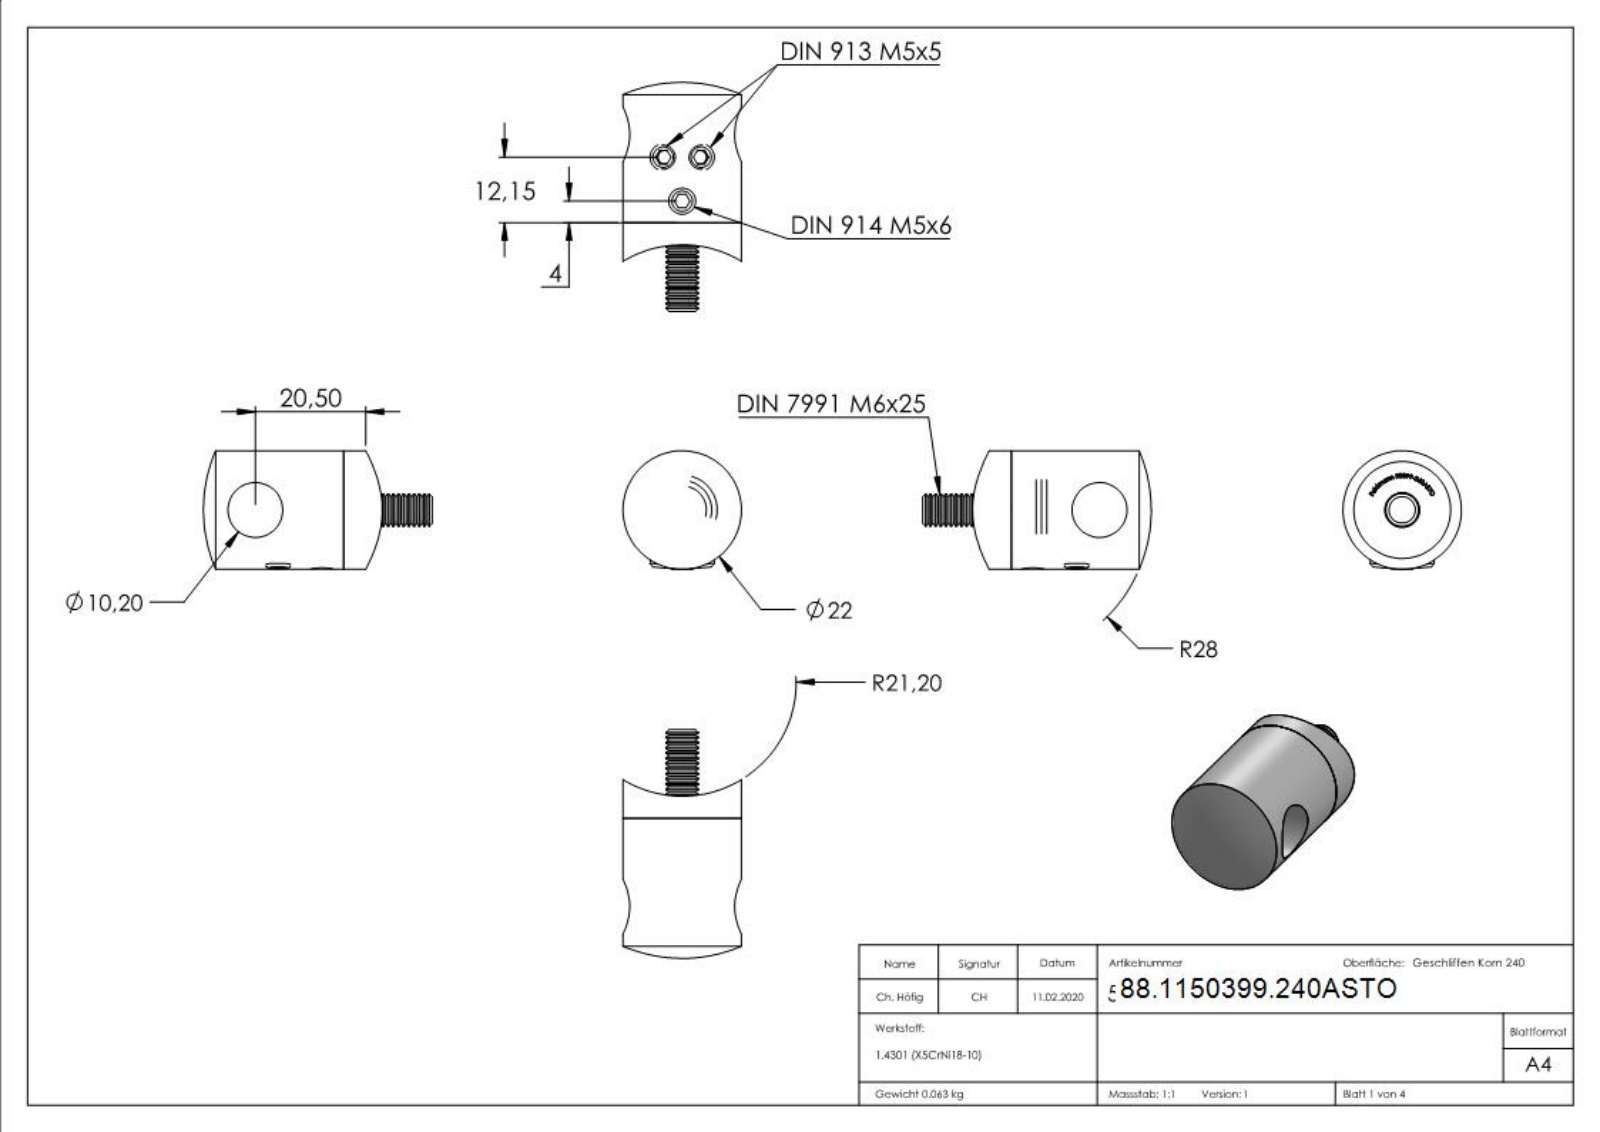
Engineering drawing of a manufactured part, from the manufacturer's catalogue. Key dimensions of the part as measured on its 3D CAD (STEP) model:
Part name (STEP PRODUCT): Querstabhalter Teil1 Konfig_50XXX-240ASTO Teil1 10,2; Querstabhalter Teil2 Konfig; socket countersunk head screw_din; DIN913 (+7 more)
STEP written by: SolidWorks 2015 (CONFIG_CONTROL_DESIGN)
Units: millimetres
Bodies: 6 solids, 436 faces (201 planar, 38 cylindrical, 197 other)
Overall size (bounding box): 69790.35 × 11012.2 × 5000
Volume: 8 666 mm³ · Surface area: 6 298 mm²
Round holes (diameter × count): ⌀4.2 ×3, ⌀6.5 ×1, ⌀10.2 ×1, ⌀12 ×1, ⌀18 ×1
Round bosses / shafts (diameter × count): ⌀5 ×3, ⌀22 ×1, ⌀11.9 ×1, ⌀11.57 ×1, ⌀6 ×1
Partial cylindrical surfaces — rounded edges, fillets, slot ends (radius × count): R21.2 ×1
Main face-to-face distances: 2.1, 10.65, 8.55, 2.5, 9.6, 7.5, 1.05, 14.35, 16.45, 23.95
